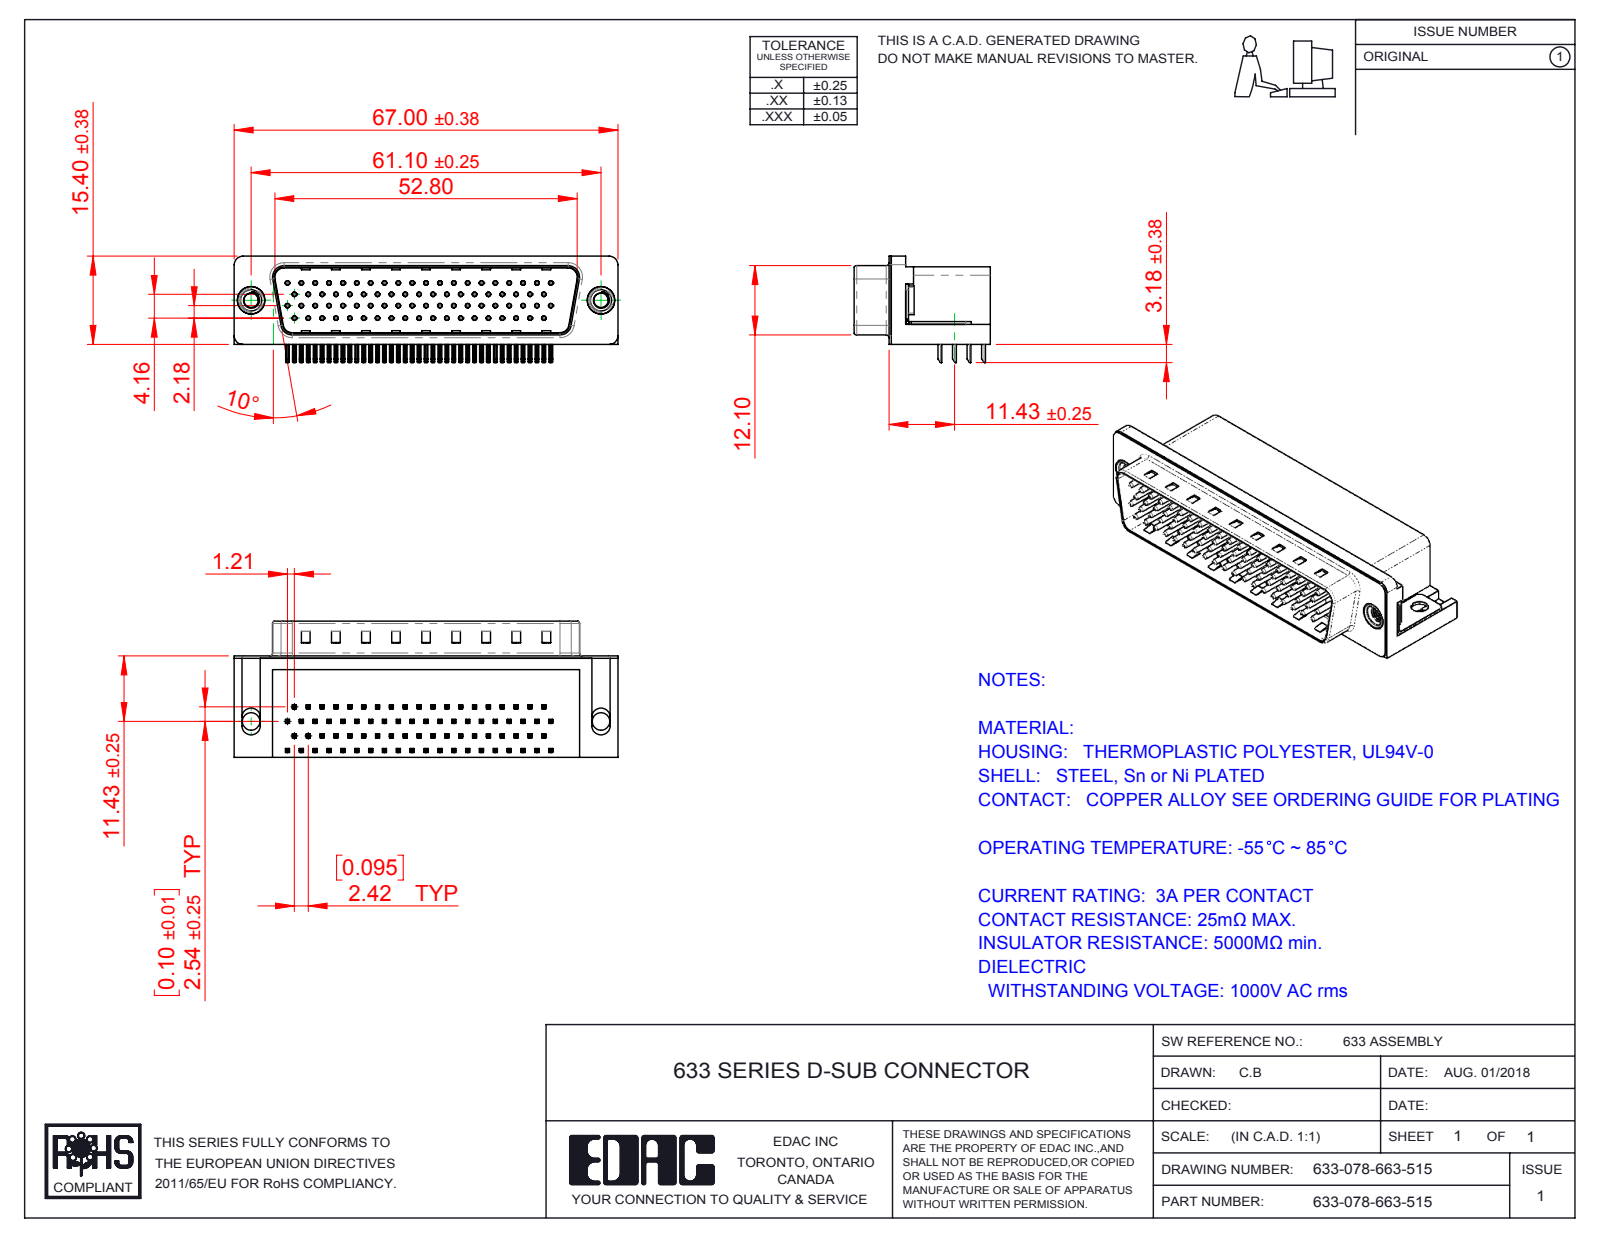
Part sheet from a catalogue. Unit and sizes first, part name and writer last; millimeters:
Units: millimetres
Overall size (bounding box): 67 × 23.8 × 18.58
Round holes (diameter × count): ⌀0.35 ×78, ⌀0.8 ×78, ⌀2.5 ×2, ⌀3.05 ×2, ⌀4 ×2, ⌀4.8 ×2, ⌀5 ×2
Round bosses / shafts (diameter × count): ⌀0.75 ×78, ⌀4.9 ×2, ⌀4.75 ×2, ⌀3.9 ×2
Partial cylindrical surfaces — rounded edges, fillets, slot ends (radius × count): R0.25 ×320, R0.12 ×156, R1 ×16, R0.5 ×9, R1.6 ×8, R1.5 ×6, R0.45 ×4, R0.9 ×4
Main face-to-face distances: 0.4, 13.2, 17.3, 11.7, 13.35, 2.05, 13.75, 1.65, 1.85, 11.9
Hole centre spacings: 2.42, 4.84, 7.26, 9.68, 6.26, 7.13, 12.1, 8.62
Volume: 14 605 mm³ · Surface area: 16 339 mm²
Bodies: 84 solids, 6274 faces (3979 planar, 1782 cylindrical, 513 other)
Part name (STEP PRODUCT): 633-078-663-515; 633 Contact Top 78; 633 Contact Top_78 Contact; 633 Shell_78 Contact (+5 more)
STEP written by: SolidWorks 2016 (CONFIG_CONTROL_DESIGN)
